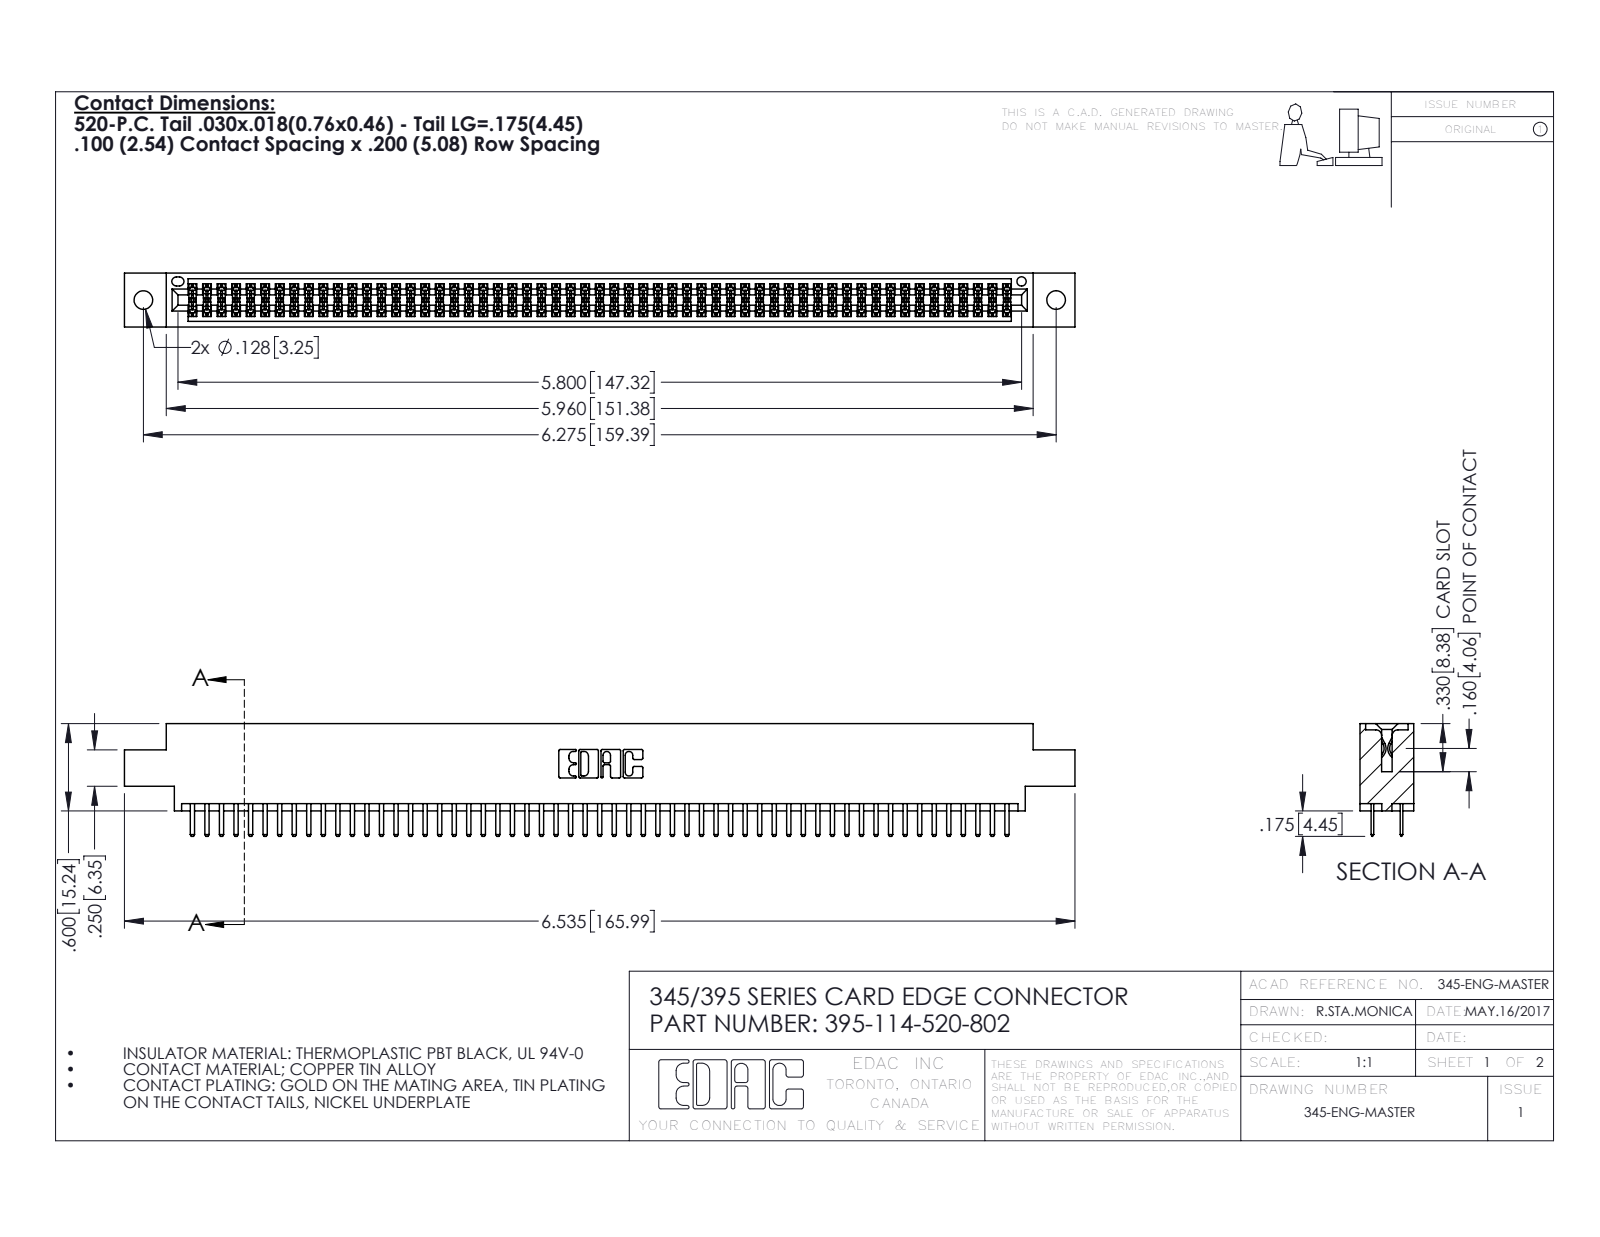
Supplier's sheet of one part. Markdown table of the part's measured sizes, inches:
| quantity | value |
| --- | --- |
| part name | 345 Part_0.170 Offset - 0.128 Dia; 345-292-001_345-293-120; 395-114-520-802 |
| STEP written by | SolidWorks 2016 (CONFIG_CONTROL_DESIGN) |
| units | inches |
| bodies | 115 solids, 6286 faces (4074 planar, 2212 cylindrical, 0 other) |
| overall size | 6.535 × 0.775 × 0.37 |
| volume | 0.98 in³ |
| surface area | 36.89 in² |
| round holes (diameter × count) | 0.128 × 2, 0.064 × 1 |
| partial cylindrical surfaces (radius × count) | 0.006 × 171, 0.01 × 118, 0.01 × 22, 0.007 × 6, 0.031 × 6, 0.026 × 3, 0.014 × 2, 0.019 × 2 |
| main face-to-face distances | 0.072, 0.298, 0.2, 0.37, 0.098, 0.272, 0.025, 0.225, 0.022, 0.072 |
| hole center spacings | 0.27, 6.039, 6.275 |
